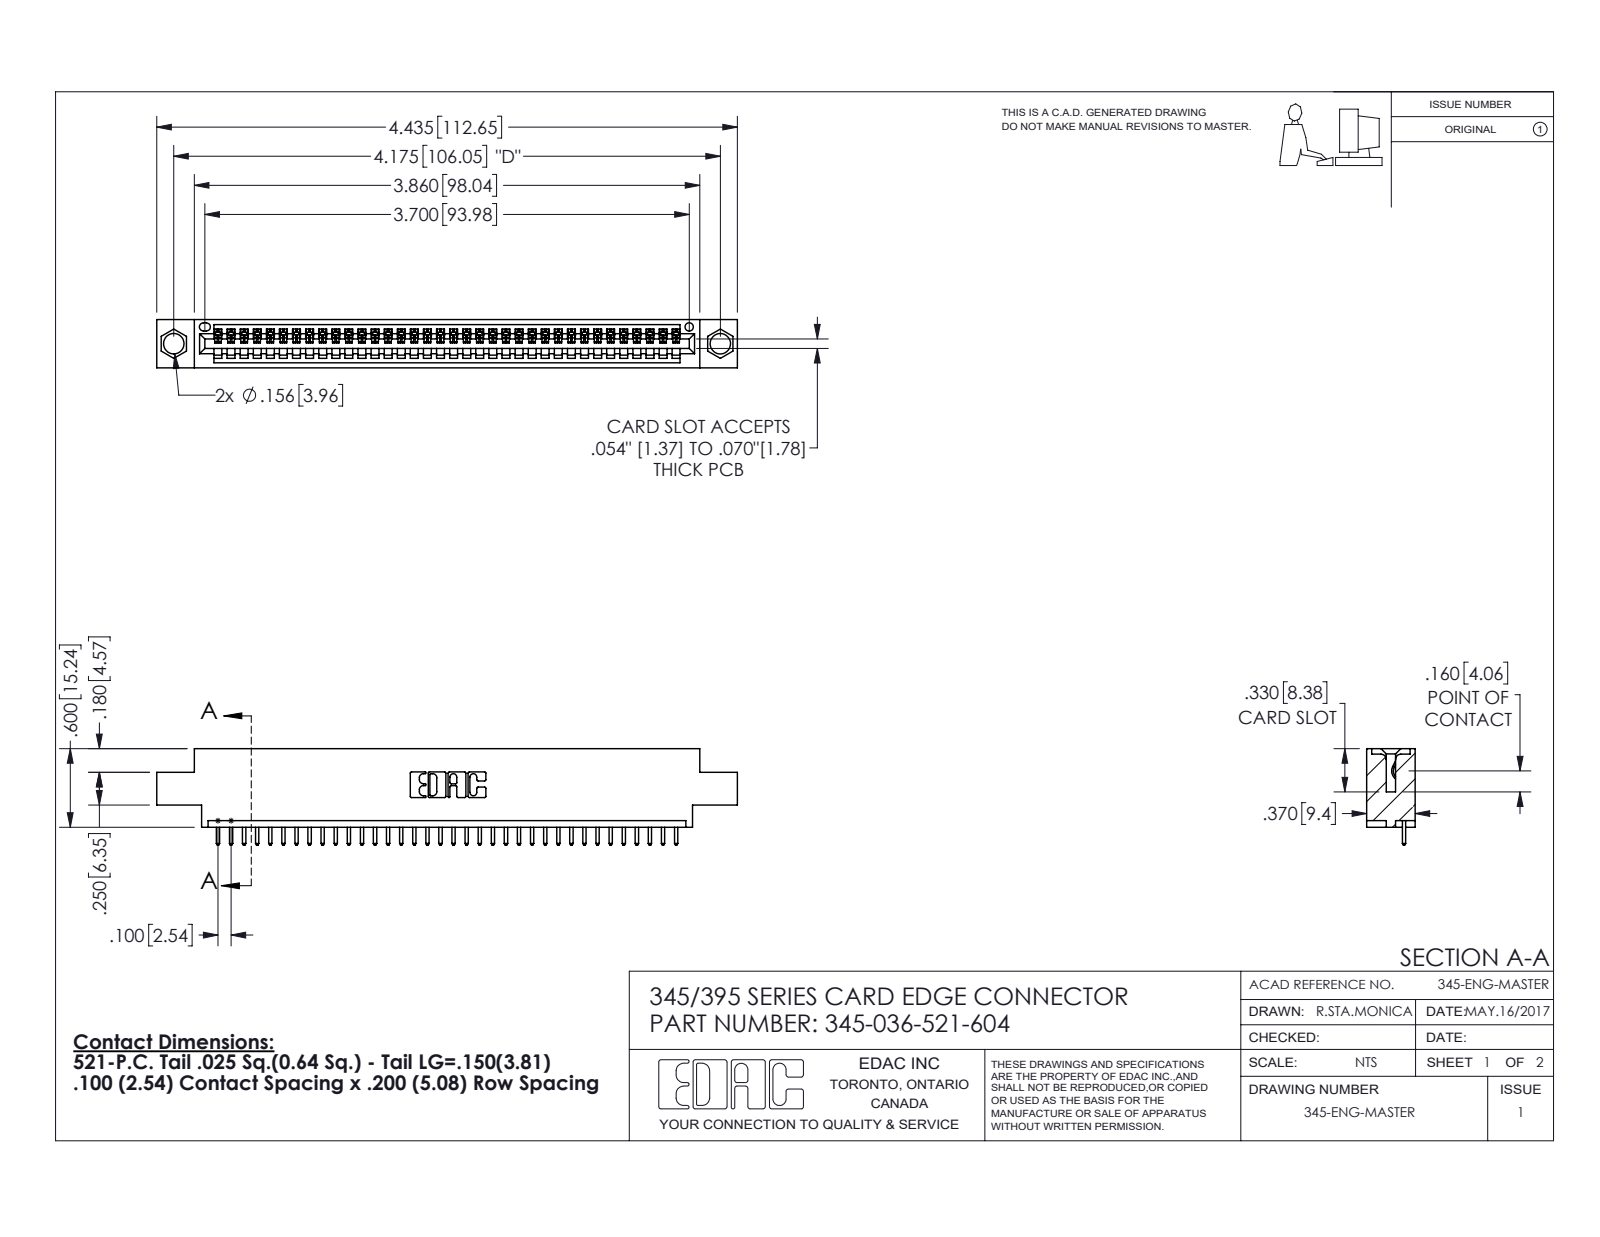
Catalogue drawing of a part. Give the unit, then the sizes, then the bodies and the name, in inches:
Units: inches
Overall size (bounding box): 4.435 × 0.737 × 0.37
Round holes (diameter × count): ⌀0.156 ×2, ⌀0.064 ×1
Partial cylindrical surfaces — rounded edges, fillets, slot ends (radius × count): R0.006 ×72, R0.01 ×72, R0.01 ×22, R0.007 ×6, R0.031 ×6, R0.026 ×3, R0.031 ×2, R0.04 ×2
Main face-to-face distances: 0.072, 0.298, 0.37, 0.2, 0.098, 0.272, 0.025, 0.225, 0.175, 0.149
Hole centre spacings: 0.27, 3.939, 4.175
Volume: 0.631 in³ · Surface area: 20.46 in²
Bodies: 37 solids, 2218 faces (1524 planar, 694 cylindrical, 0 other)
Part name (STEP PRODUCT): 345-292-001_345-293-121; 345 Part_0.170 Offset - 0.156 Dia-TH; 345-036-521-604
STEP written by: SolidWorks 2016 (CONFIG_CONTROL_DESIGN)
